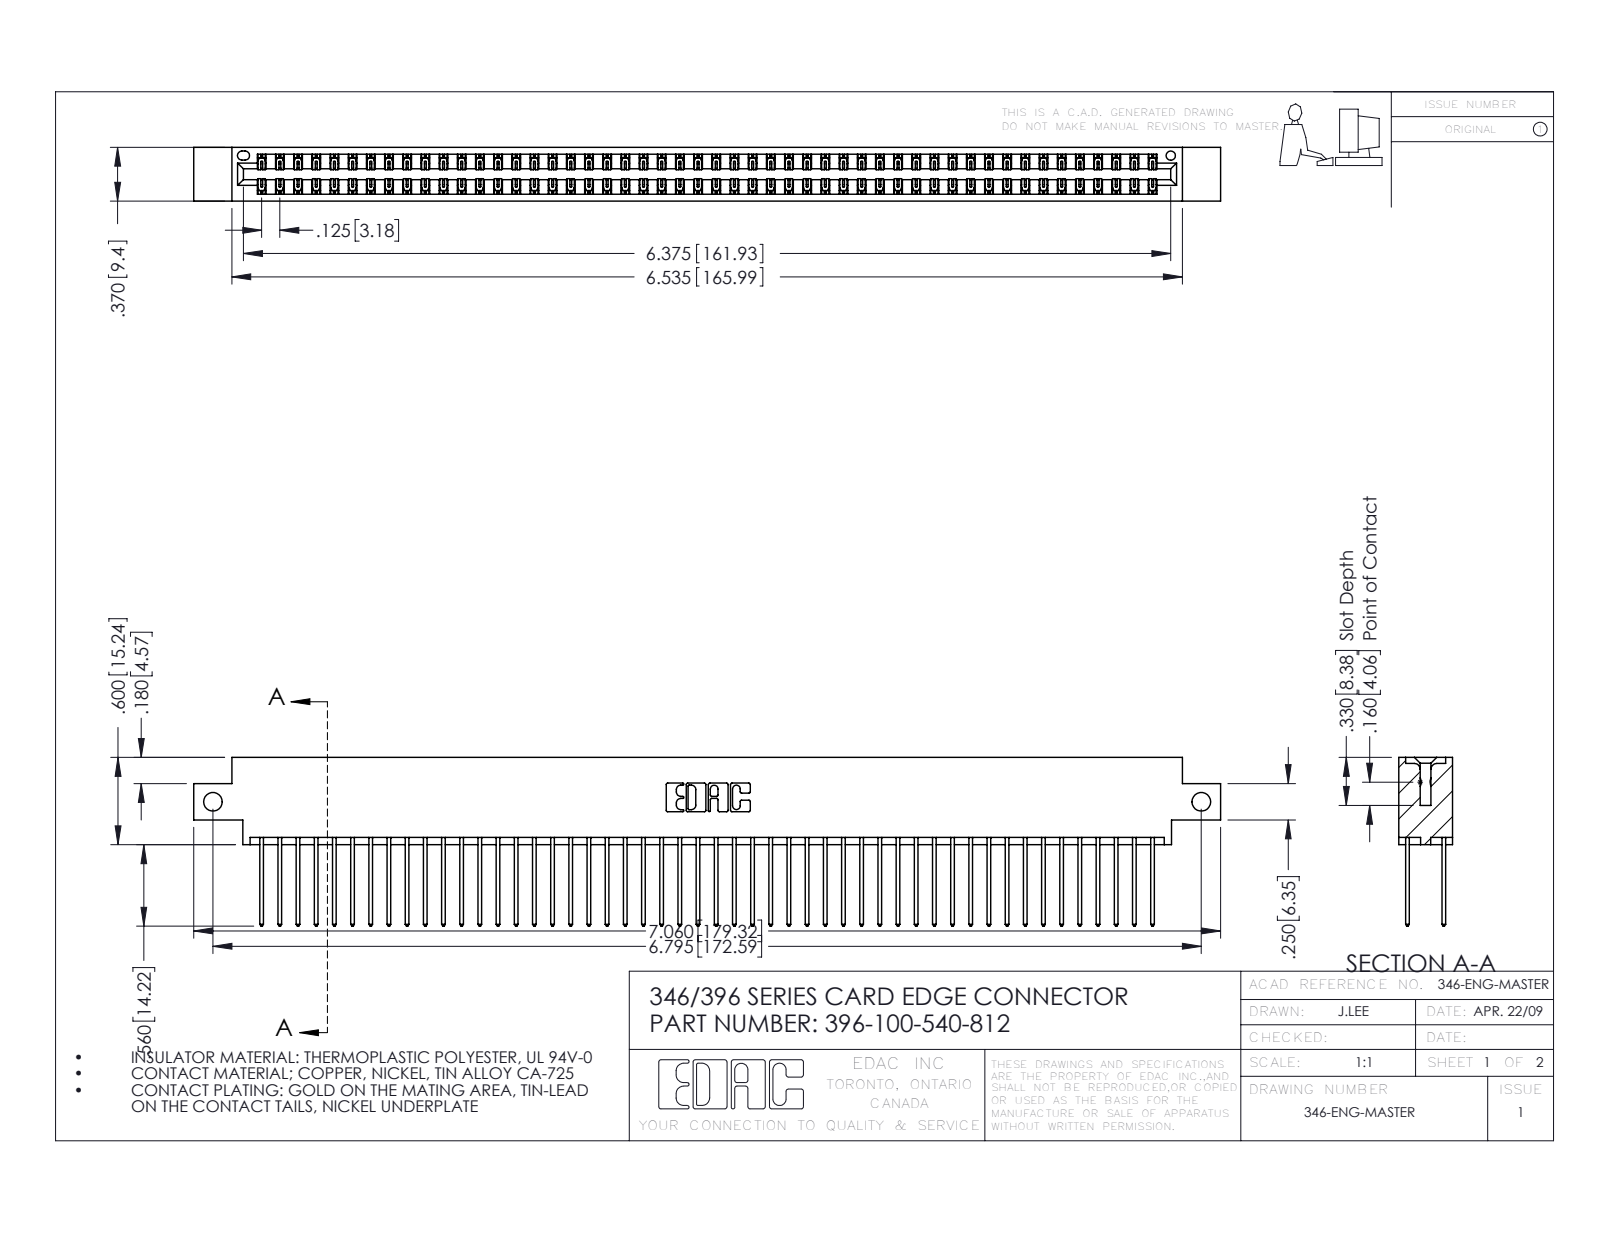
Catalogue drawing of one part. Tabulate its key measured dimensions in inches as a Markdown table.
| quantity | value |
| --- | --- |
| part name | 396-100-540-812; 346 Part_0.170 Offset - Side Mount; 345-292-001_345-293-140 |
| STEP written by | SolidWorks 2016 (CONFIG_CONTROL_DESIGN) |
| units | inches |
| bodies | 101 solids, 5326 faces (3580 planar, 1746 cylindrical, 0 other) |
| overall size | 7.06 × 1.16 × 0.37 |
| volume | 1.079 in³ |
| surface area | 40.72 in² |
| round holes (diameter × count) | 0.128 × 2, 0.064 × 1 |
| partial cylindrical surfaces (radius × count) | 0.006 × 150, 0.01 × 100, 0.01 × 22, 0.007 × 6, 0.031 × 6, 0.026 × 3, 0.014 × 2, 0.022 × 2 |
| main face-to-face distances | 0.048, 0.322, 0.25, 0.072, 0.298, 0.025, 0.37, 0.275, 0.148, 0.222 |
| hole center spacings | 6.795 |
